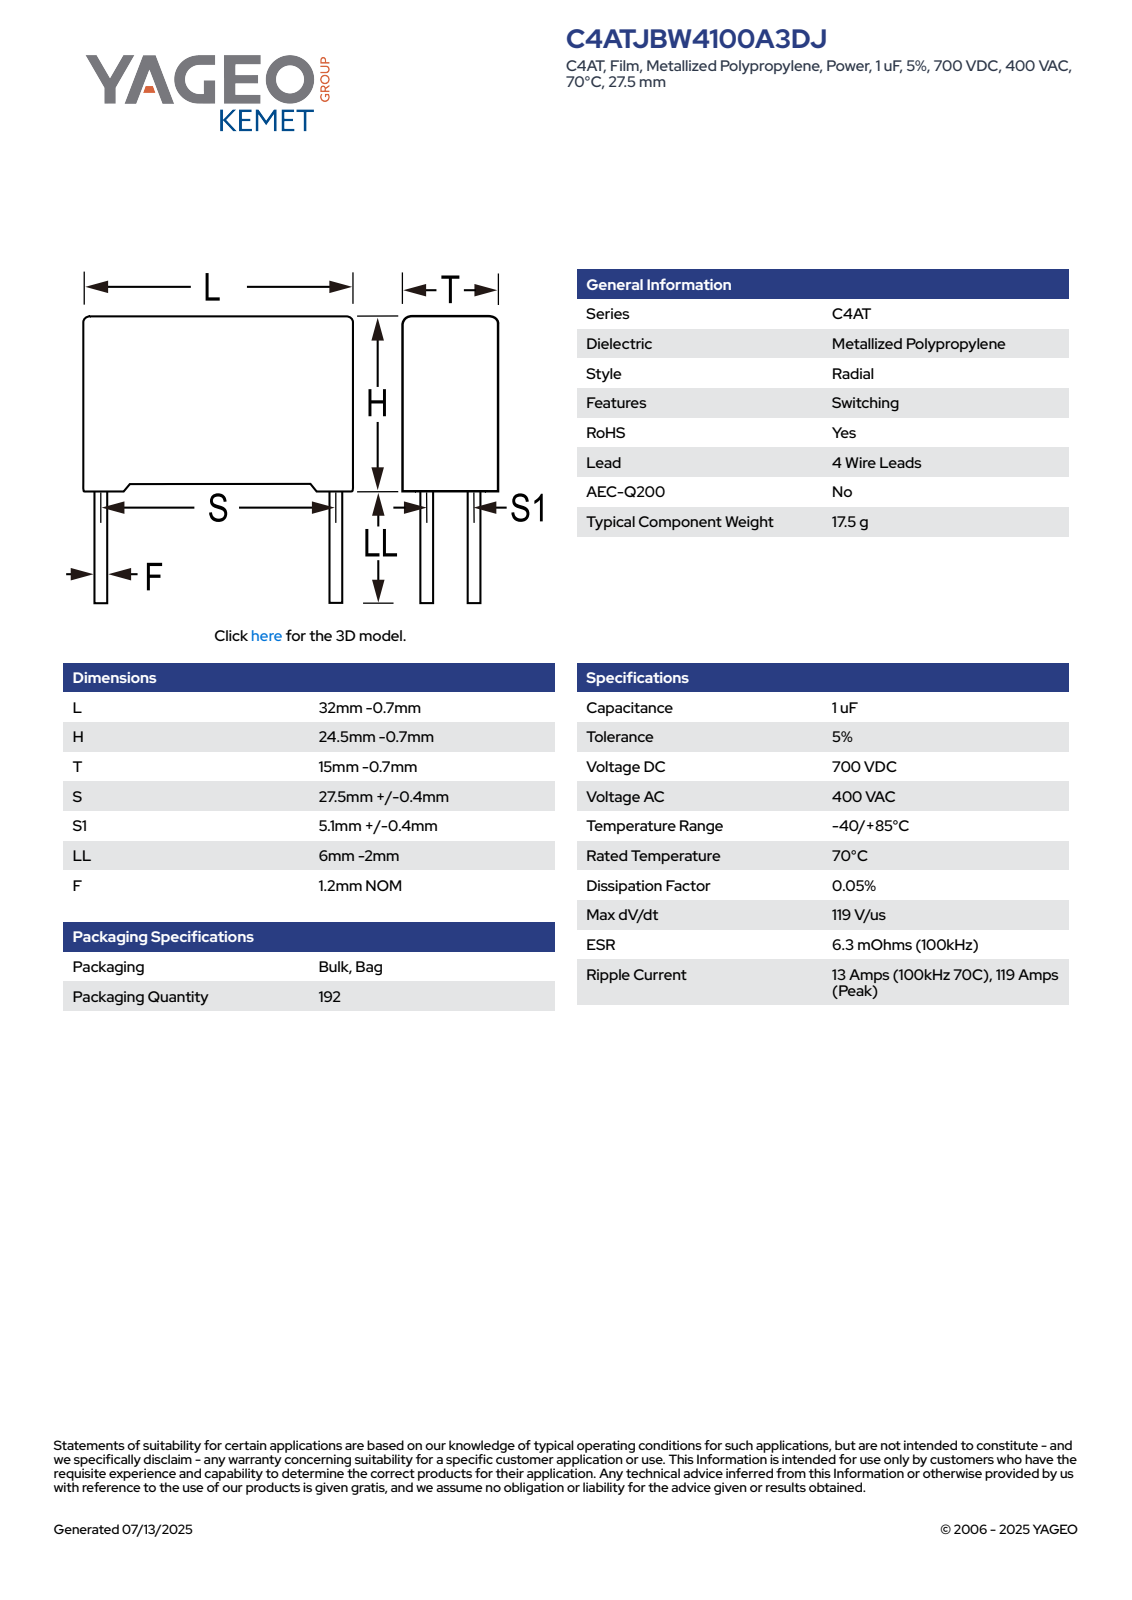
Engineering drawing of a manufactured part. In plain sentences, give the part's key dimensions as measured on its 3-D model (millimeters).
The part is named "CFP_RB4_32X24.5X15_L31.3H23.8T14.3S27.5S15.1LL4F1.2". Its 3-D file was written by "SolidWorks 2014 (AUTOMOTIVE_DESIGN)". It is 4 solids with 87 faces: 79 planar, 8 cylindrical and 0 other. Overall it measures 31.3 by 27.8 by 14.3 millimeters. Its volume is 10 393 cubic millimeters and its surface area 3 210 square millimeters. Round bosses or shafts: 4 of diameter 1.2. The main face-to-face distances are 14.3, 23.1, 31.3, 0.7, 23.8, 0.88, 30.42, 13.42, 29.54, 12.54.
